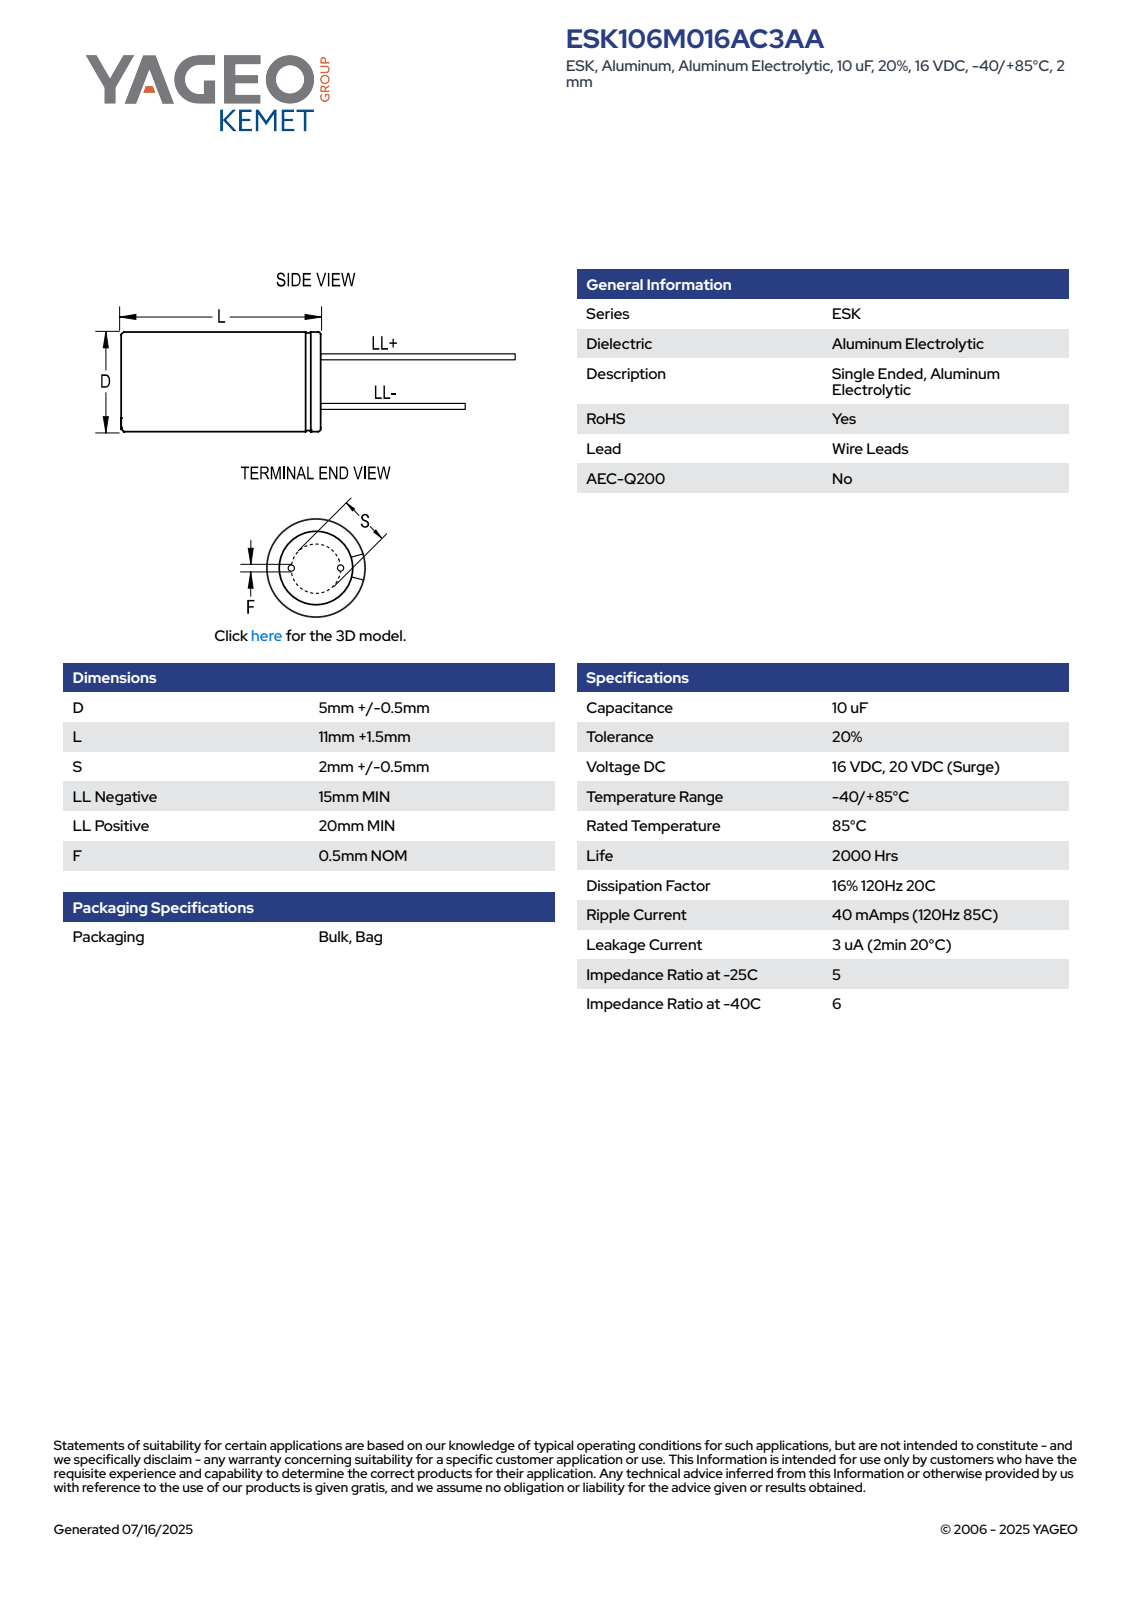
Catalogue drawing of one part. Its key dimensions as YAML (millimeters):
part_name: "CAR_KLP_5X11_D5.5L12.5S2F0.5"
step_written_by: "SolidWorks 2014 (AUTOMOTIVE_DESIGN)"
units: millimeters
bodies: {solids: 4, faces: 75, planar: 61, cylindrical: 8, other: 6}
overall_size: [32.51, 5.5, 5.5]
volume: 302
surface_area: 325
round_bosses_or_shafts:
  - {diameter: 0.5, count: 2}
  - {diameter: 5.5, count: 1}
face_to_face_distances: [12.5, 12.51, 27.51, 32.51, 27.5, 32.5, 15, 20, 5, 0.74]
